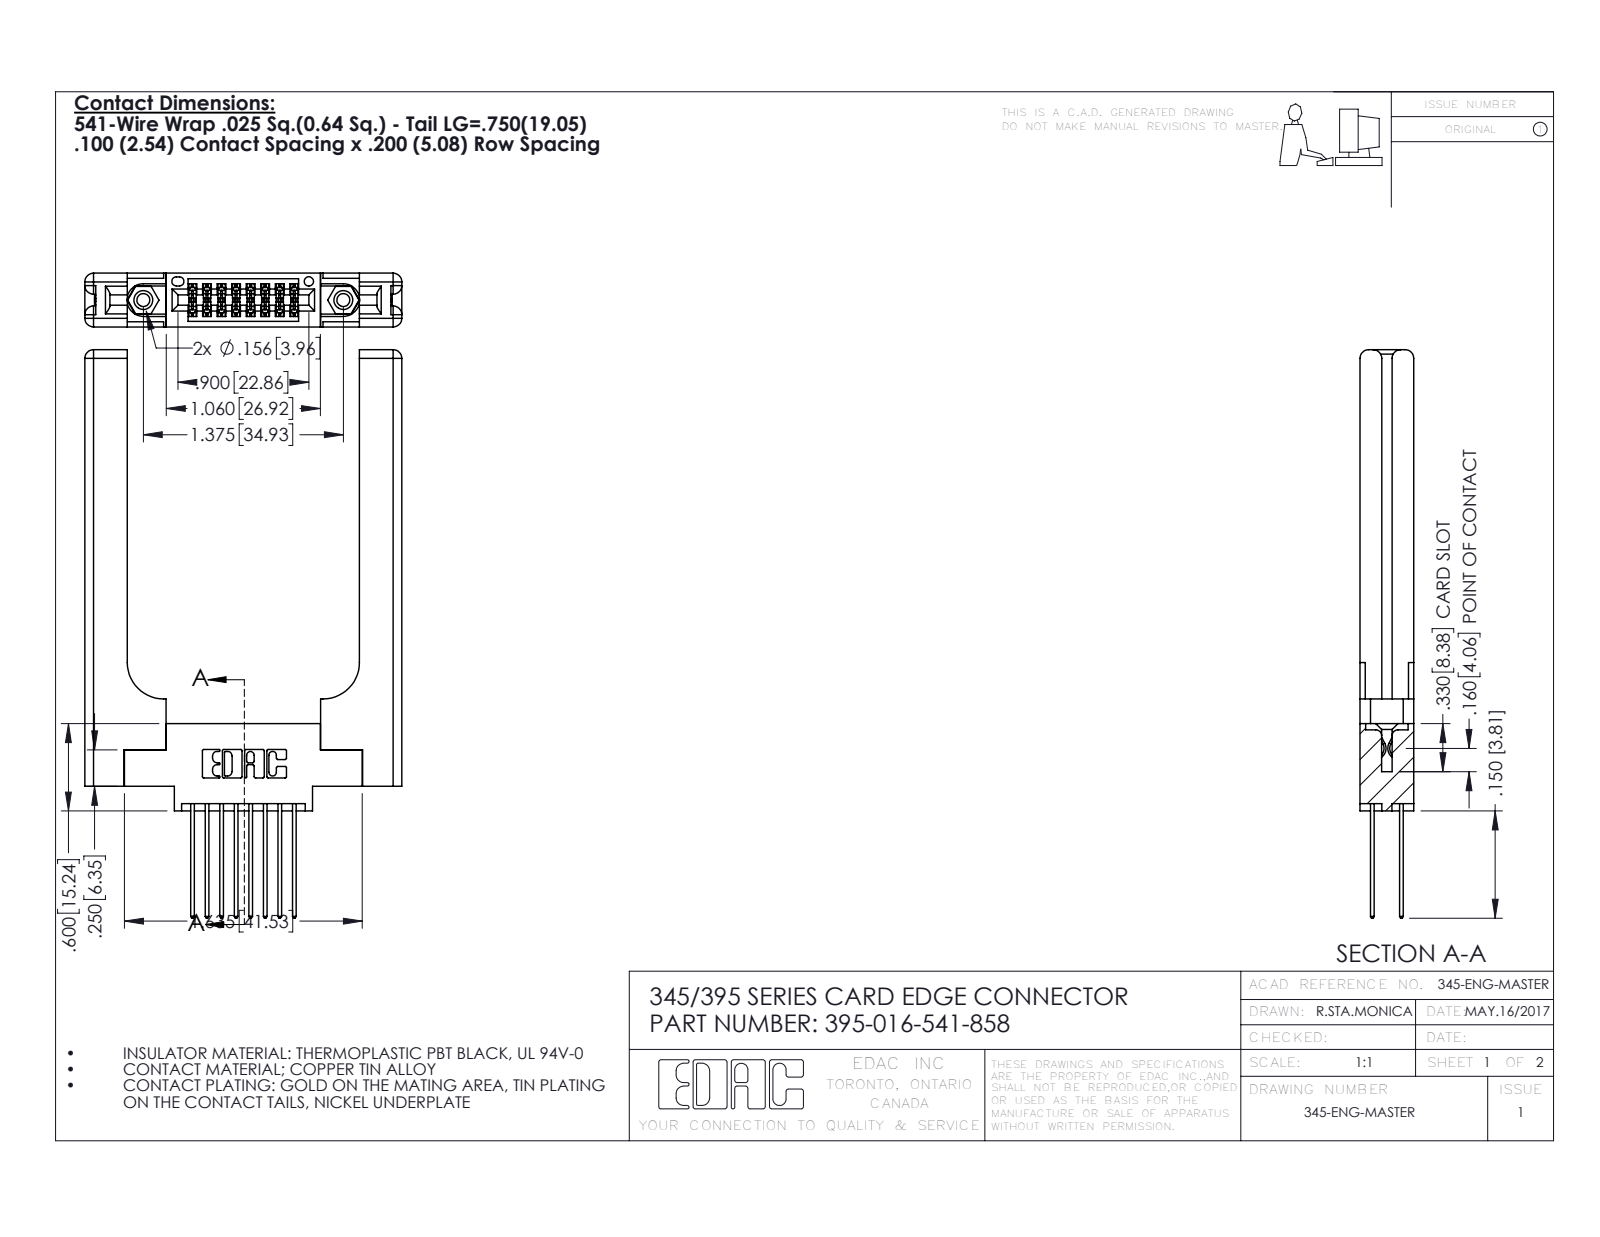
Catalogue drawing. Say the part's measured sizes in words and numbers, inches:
The part is named "345-292-001_345-293-141; 345-250-001_345-250-001-102; 345-220-058_345-220-058; 395-016-541-858 (+1 more)". Its 3-D file was written by "SolidWorks 2016 (CONFIG_CONTROL_DESIGN)". It is 21 solids with 1186 faces: 760 planar, 366 cylindrical and 60 other. Overall it measures 3.907 by 2.179 by 0.37 inches. Its volume is 0.825 cubic inches and its surface area 19.26 square inches. Round holes: 2 of diameter 0.089, 2 of diameter 0.125, 2 of diameter 0.156, 1 of diameter 0.064. Round bosses or shafts: 2 of diameter 0.155. Partial cylindrical surfaces (rounded edges, fillets, slot ends): 24 of radius 0.006, 22 of radius 0.01, 16 of radius 0.01, 16 of radius 0.06, 6 of radius 0.007, 6 of radius 0.031, 3 of radius 0.026, 2 of radius 0.014. The main face-to-face distances are 0.37, 0.072, 0.148, 0.15, 0.077, 0.298, 0.22, 0.123, 0.225, 0.098. The hole center spacings are 0.27, 1.144, 1.375.
